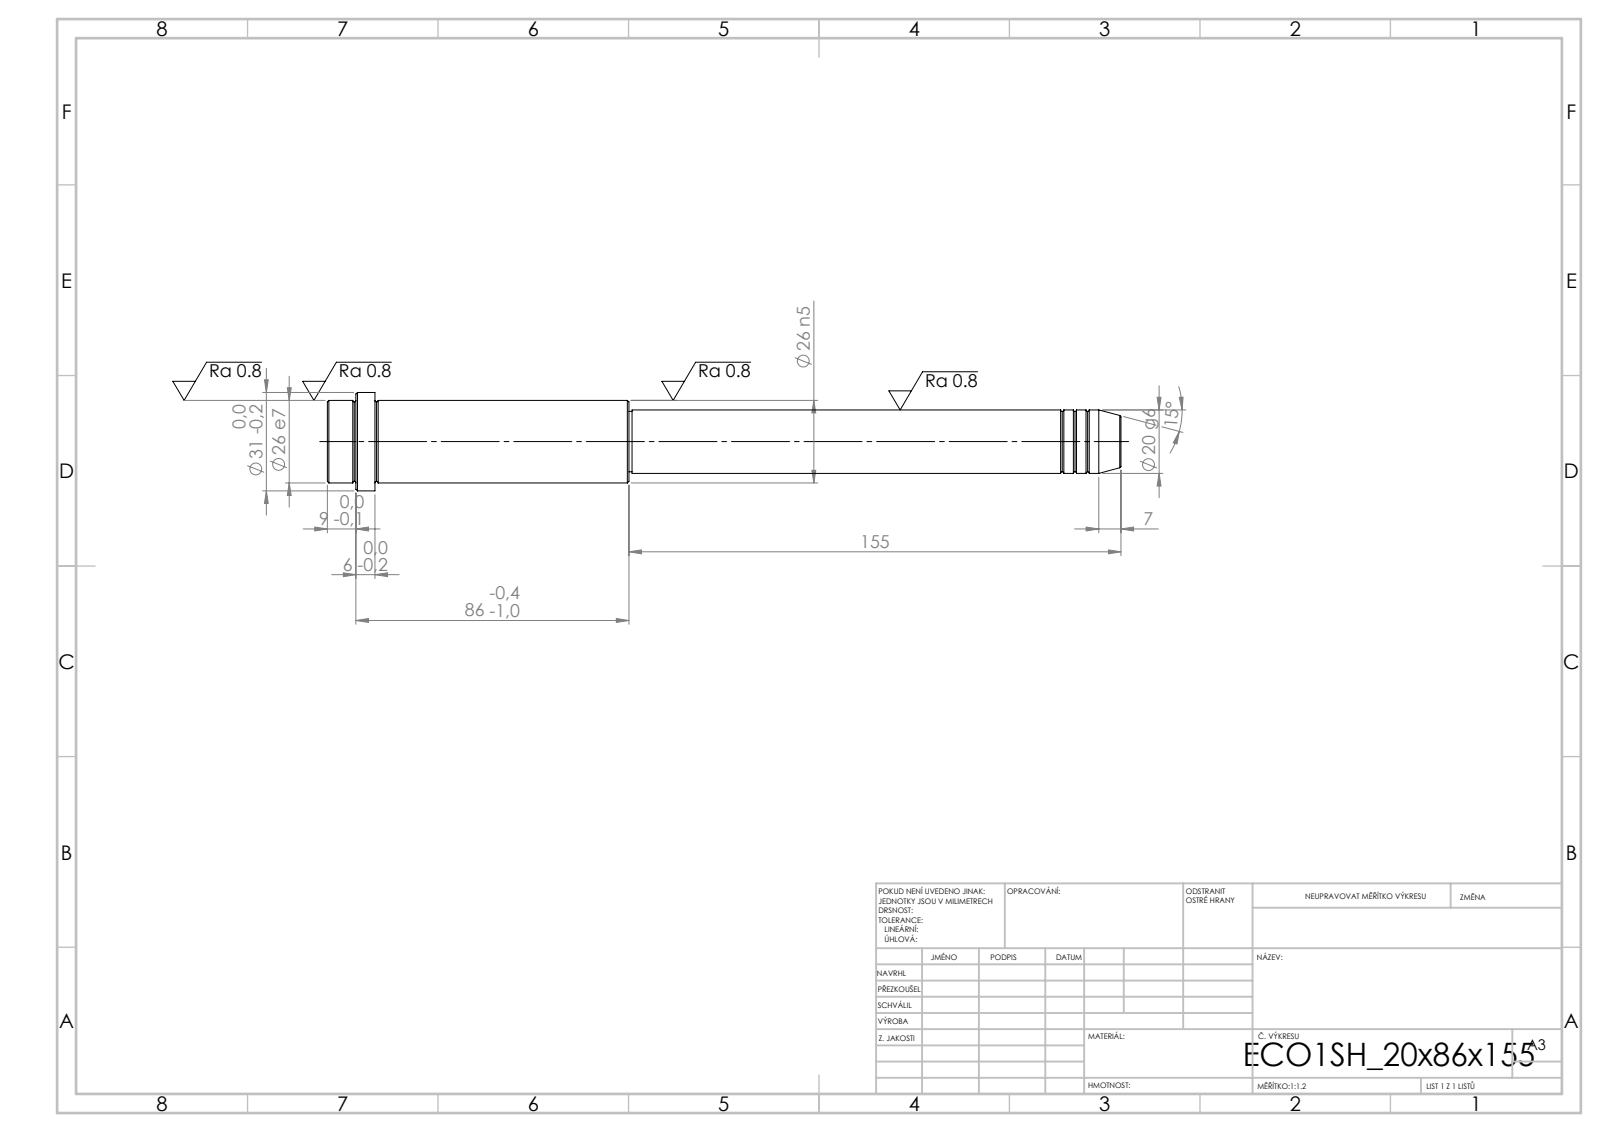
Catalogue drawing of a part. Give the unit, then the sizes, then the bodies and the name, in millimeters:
Units: millimetres
Overall size (bounding box): 250 × 31 × 31
Round bosses / shafts (diameter × count): ⌀31 ×1, ⌀26 ×1, ⌀20 ×1, ⌀19 ×1
Main face-to-face distances: 15, 80, 95, 155, 235, 250, 241, 86, 6, 9
Volume: 99 889 mm³ · Surface area: 19 129 mm²
Bodies: 1 solid, 52 faces (6 planar, 16 cylindrical, 30 other)
STEP written by: SolidWorks 2019 (CONFIG_CONTROL_DESIGN)
